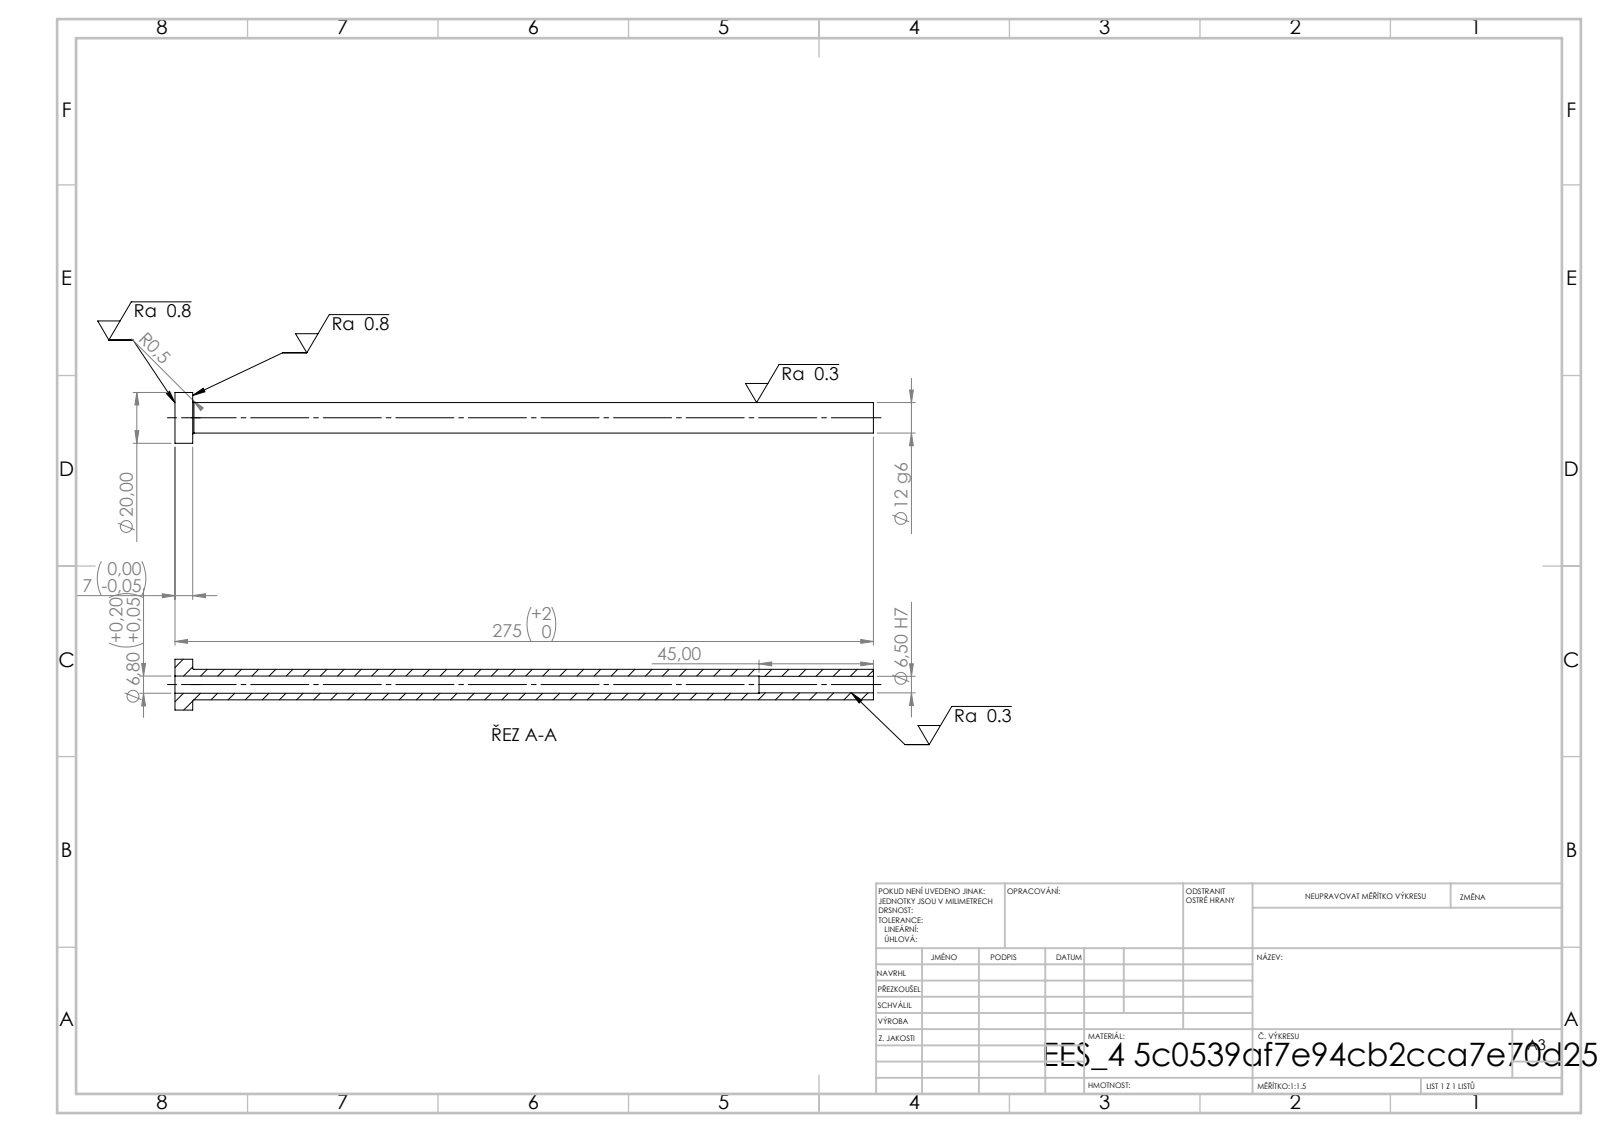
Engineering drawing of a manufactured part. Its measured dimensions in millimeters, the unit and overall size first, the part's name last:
Units: millimetres
Overall size (bounding box): 275 × 20 × 20
Round holes (diameter × count): ⌀6.5 ×1, ⌀6.8 ×1
Round bosses / shafts (diameter × count): ⌀20 ×1, ⌀12 ×1
Main face-to-face distances: 7, 275, 268, 230, 223, 45
Volume: 22 665 mm³ · Surface area: 16 930 mm²
Bodies: 1 solid, 14 faces (4 planar, 8 cylindrical, 2 other)
STEP written by: SolidWorks 2019 (CONFIG_CONTROL_DESIGN)
